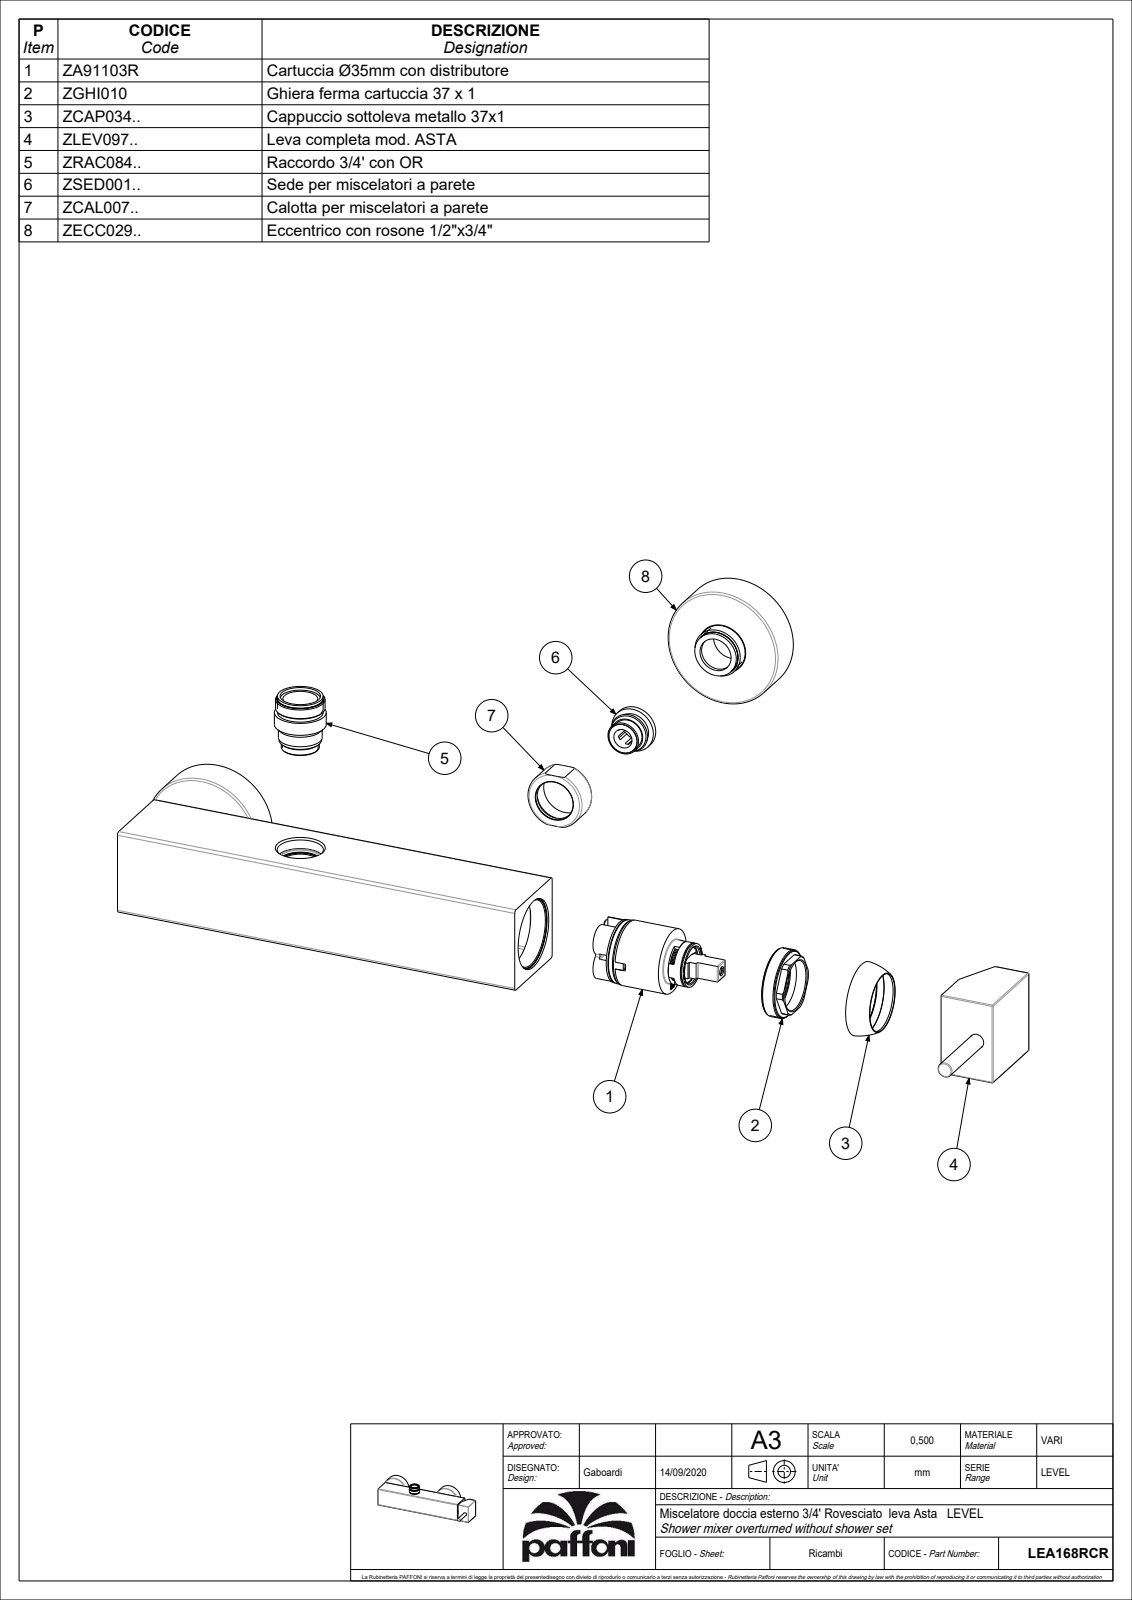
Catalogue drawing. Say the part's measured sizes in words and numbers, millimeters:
The part is named "LEA168RCR". Its 3-D file was written by "CREO PARAMETRIC BY PTC INC, 2020044 (CONFIG_CONTROL_DESIGN)". It is 1 solid with 1586 faces: 788 planar, 469 cylindrical and 329 other. Overall it measures 273.25 by 120.75 by 74 millimeters. Its volume is 258 898 cubic millimeters and its surface area 171 832 square millimeters. Round holes: 3 of diameter 9, 3 of diameter 10.5, 3 of diameter 12, 2 of diameter 4, 2 of diameter 7, 2 of diameter 8, 2 of diameter 18, 2 of diameter 21.6, 2 of diameter 24.5, 2 of diameter 25, 2 of diameter 37, 2 of diameter 62.3. Round bosses or shafts: 3 of diameter 24, 2 of diameter 63.5, 2 of diameter 27, 2 of diameter 23.5, 2 of diameter 17.7, 1 of diameter 35, 1 of diameter 34.8, 1 of diameter 33.8. Partial cylindrical surfaces (rounded edges, fillets, slot ends): 90 of radius 1, 54 of radius 0.5, 11 of radius 0.15, 9 of radius 0.3, 4 of radius 1.5, 4 of radius 7, 2 of radius 4.5, 2 of radius 5. The main face-to-face distances are 3.75, 42.75, 46.5, 39, 3, 15, 18.75, 61.5, 57.75, 42. The hole center spacings are 0.71, 8.51, 8.6, 13.04, 13.21, 13.51, 6, 13.
